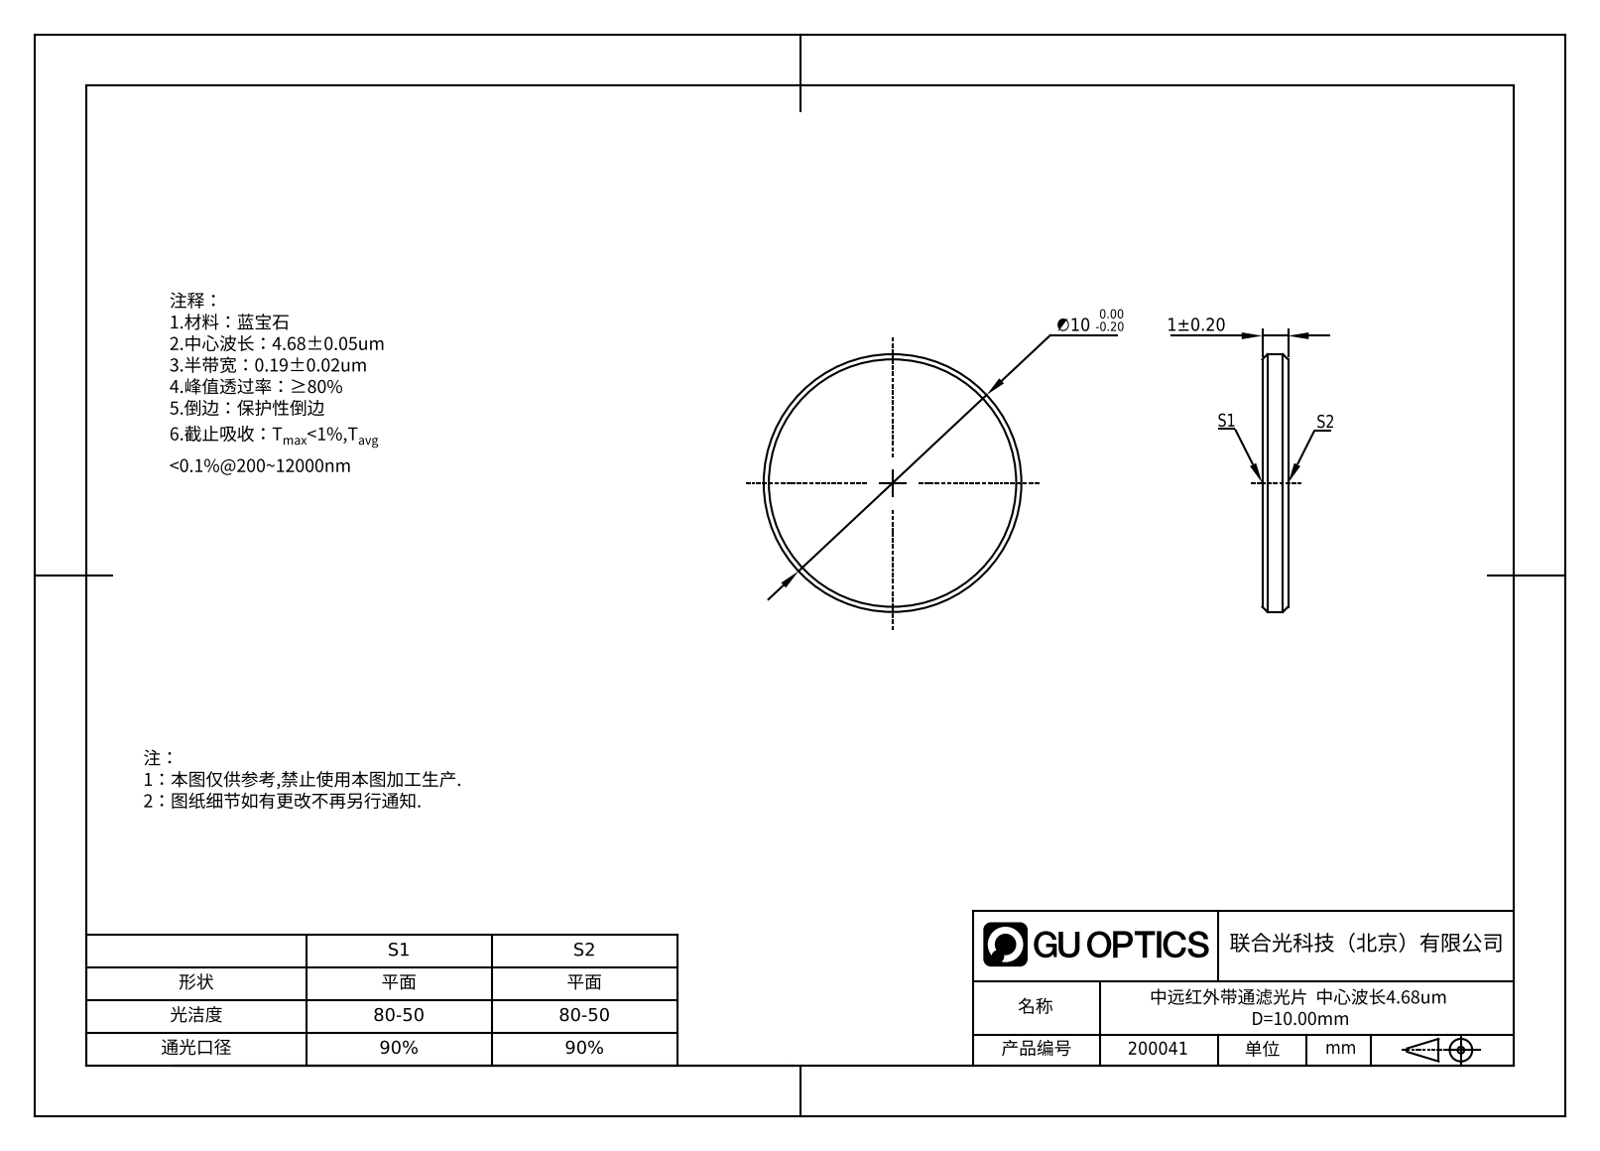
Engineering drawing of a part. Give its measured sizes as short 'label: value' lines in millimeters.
name: GNIF-070-4680-D10
written by: SolidWorks 2022 (AUTOMOTIVE_DESIGN)
unit: mm
bodies: 1 solid, 8 faces (2 planar, 2 cylindrical, 4 other)
size: 10 × 10 × 1
volume: 77 mm³; area: 181 mm²
bosses: 1× ⌀10
face distances: 1
